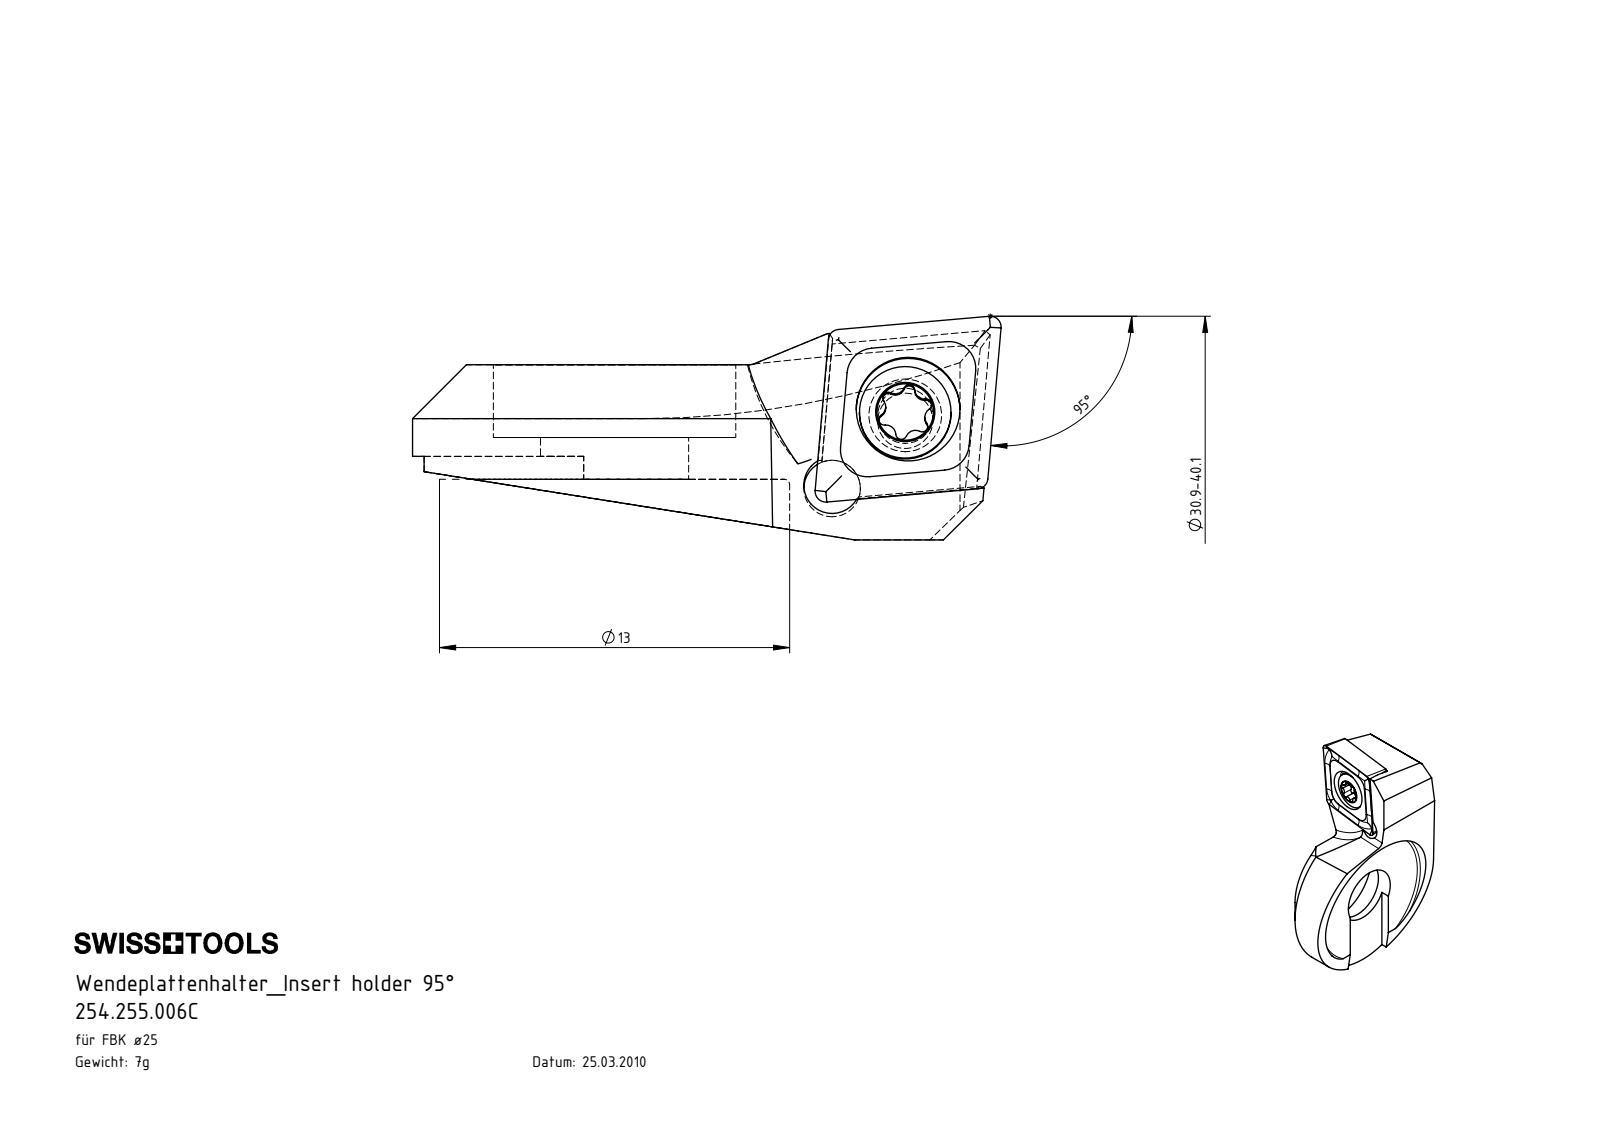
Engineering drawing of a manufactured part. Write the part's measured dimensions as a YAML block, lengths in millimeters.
part_name: "F25-WCA.002.006_C_fertigbearbeitet; CCMT060204; WCA-ER2.001.006_A; 254.255.006C"
step_written_by: "SolidWorks 2017 (CONFIG_CONTROL_DESIGN)"
units: millimeters
bodies: {solids: 5, faces: 143, planar: 49, cylindrical: 43, other: 51}
overall_size: [21.85, 15, 8.3]
volume: 875
surface_area: 1309
round_holes:
  - {diameter: 2.05, count: 1}
  - {diameter: 2.1, count: 1}
  - {diameter: 2.8, count: 1}
  - {diameter: 3.85, count: 1}
  - {diameter: 5.5, count: 1}
  - {diameter: 9, count: 1}
round_bosses_or_shafts:
  - {diameter: 3.4, count: 1}
  - {diameter: 2.5, count: 1}
partial_cylinders:
  - {radius: 0.21, count: 6}
  - {radius: 0.36, count: 5}
  - {radius: 0.5, count: 2}
  - {radius: 0.36, count: 1}
  - {radius: 1.05, count: 1}
  - {radius: 6.5, count: 1}
  - {radius: 7.5, count: 1}
  - {radius: 9, count: 1}
face_to_face_distances: [4.25, 4.15, 2.27, 2.7, 2.6, 1.55, 2.28, 3.4, 3.3, 0.7]
hole_center_spacings: [3.84, 3.99]
